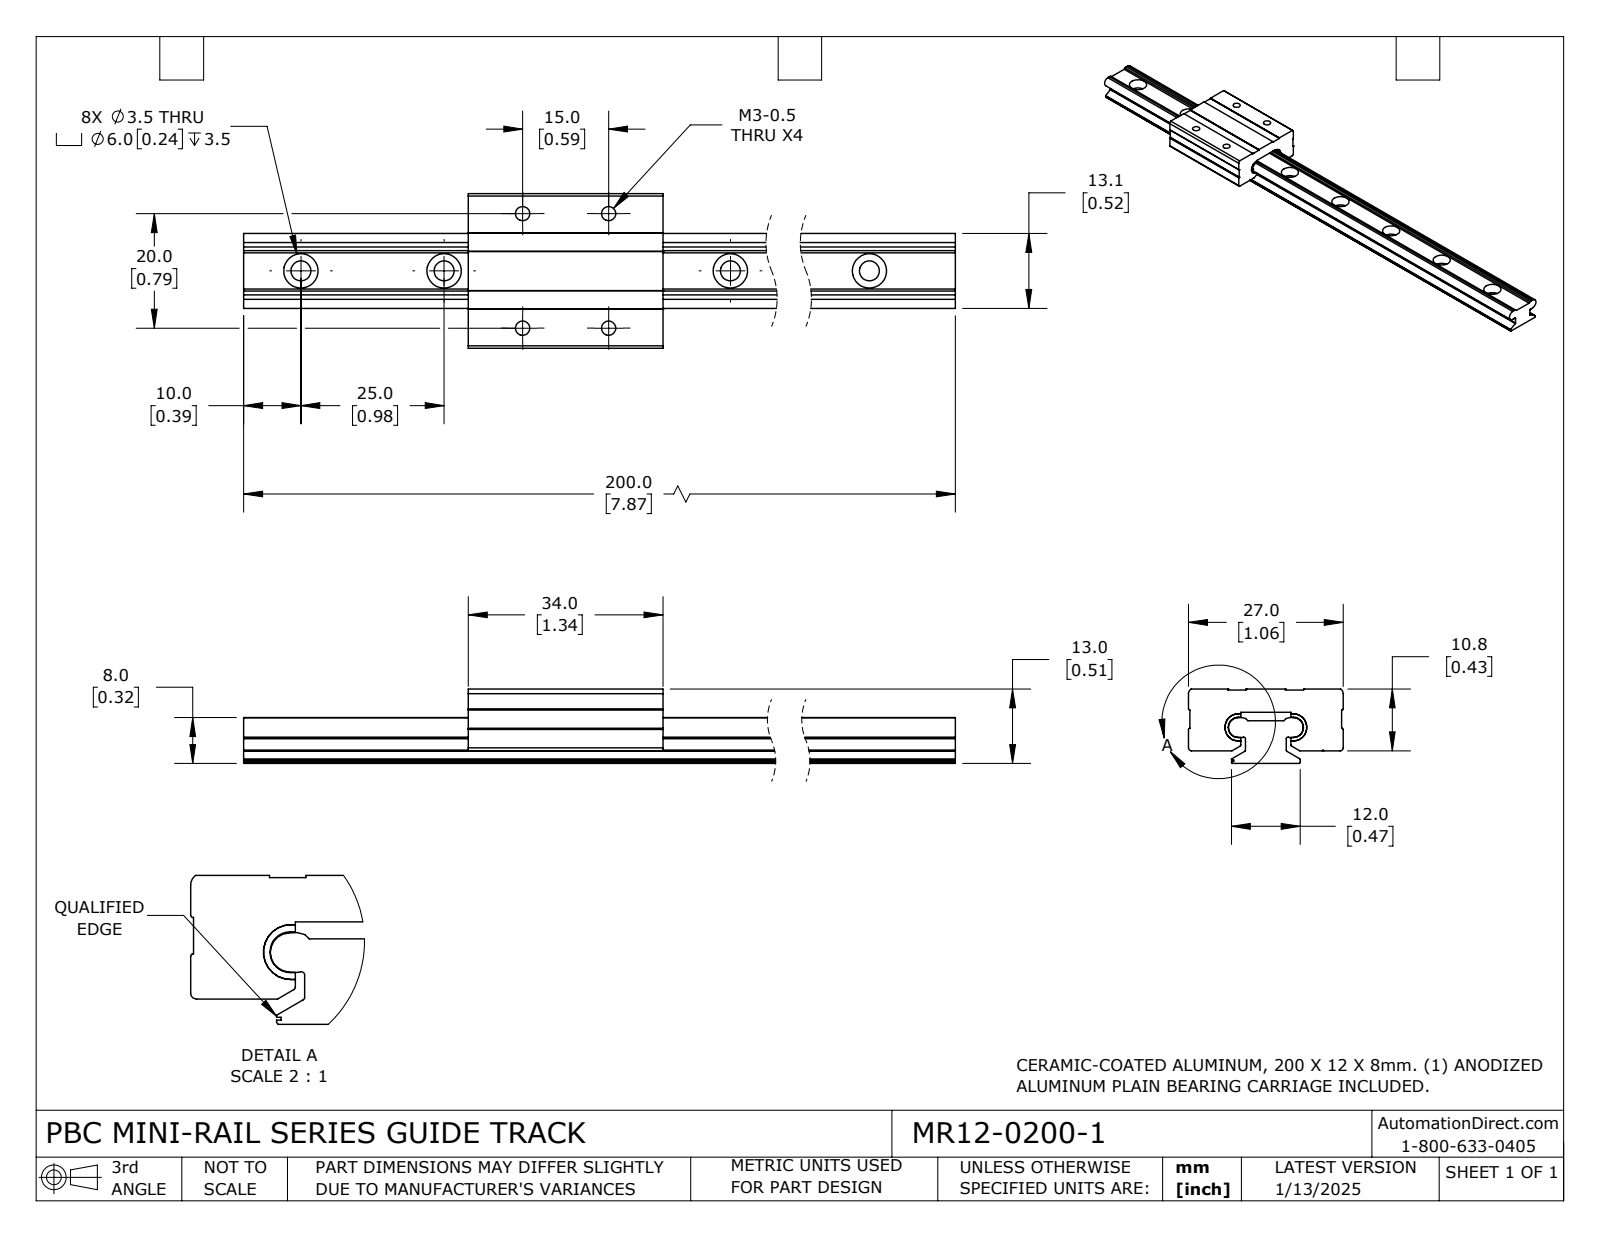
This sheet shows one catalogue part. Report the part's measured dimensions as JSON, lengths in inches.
{"part_name": "MR12-0200-1_RAILS; MR12-0200-1; MR12-0200-1_CARRIAGE", "step_written_by": "SolidWorks 2023 (CONFIG_CONTROL_DESIGN)", "units": "inches", "bodies": {"solids": 4, "faces": 167, "planar": 91, "cylindrical": 76, "other": 0}, "overall_size": [7.874, 1.063, 0.512], "volume_in3": 1.321, "surface_area_in2": 23.95, "round_holes": [[0.138, 8], [0.236, 8], [0.098, 4]], "partial_cylinders_radius": [[0.01, 9], [0.008, 8], [0.069, 4], [0.011, 2], [0.02, 2], [0.04, 2], [0.067, 2], [0.094, 2]], "face_to_face_distances": [0.293, 0.512, 0.219, 0.087, 0.206, 0.425, 0.391, 0.672, 0.28, 0.153], "hole_center_spacings": [0.984, 1.969, 2.953, 3.937, 4.921, 0.42, 0.591, 0.593]}
